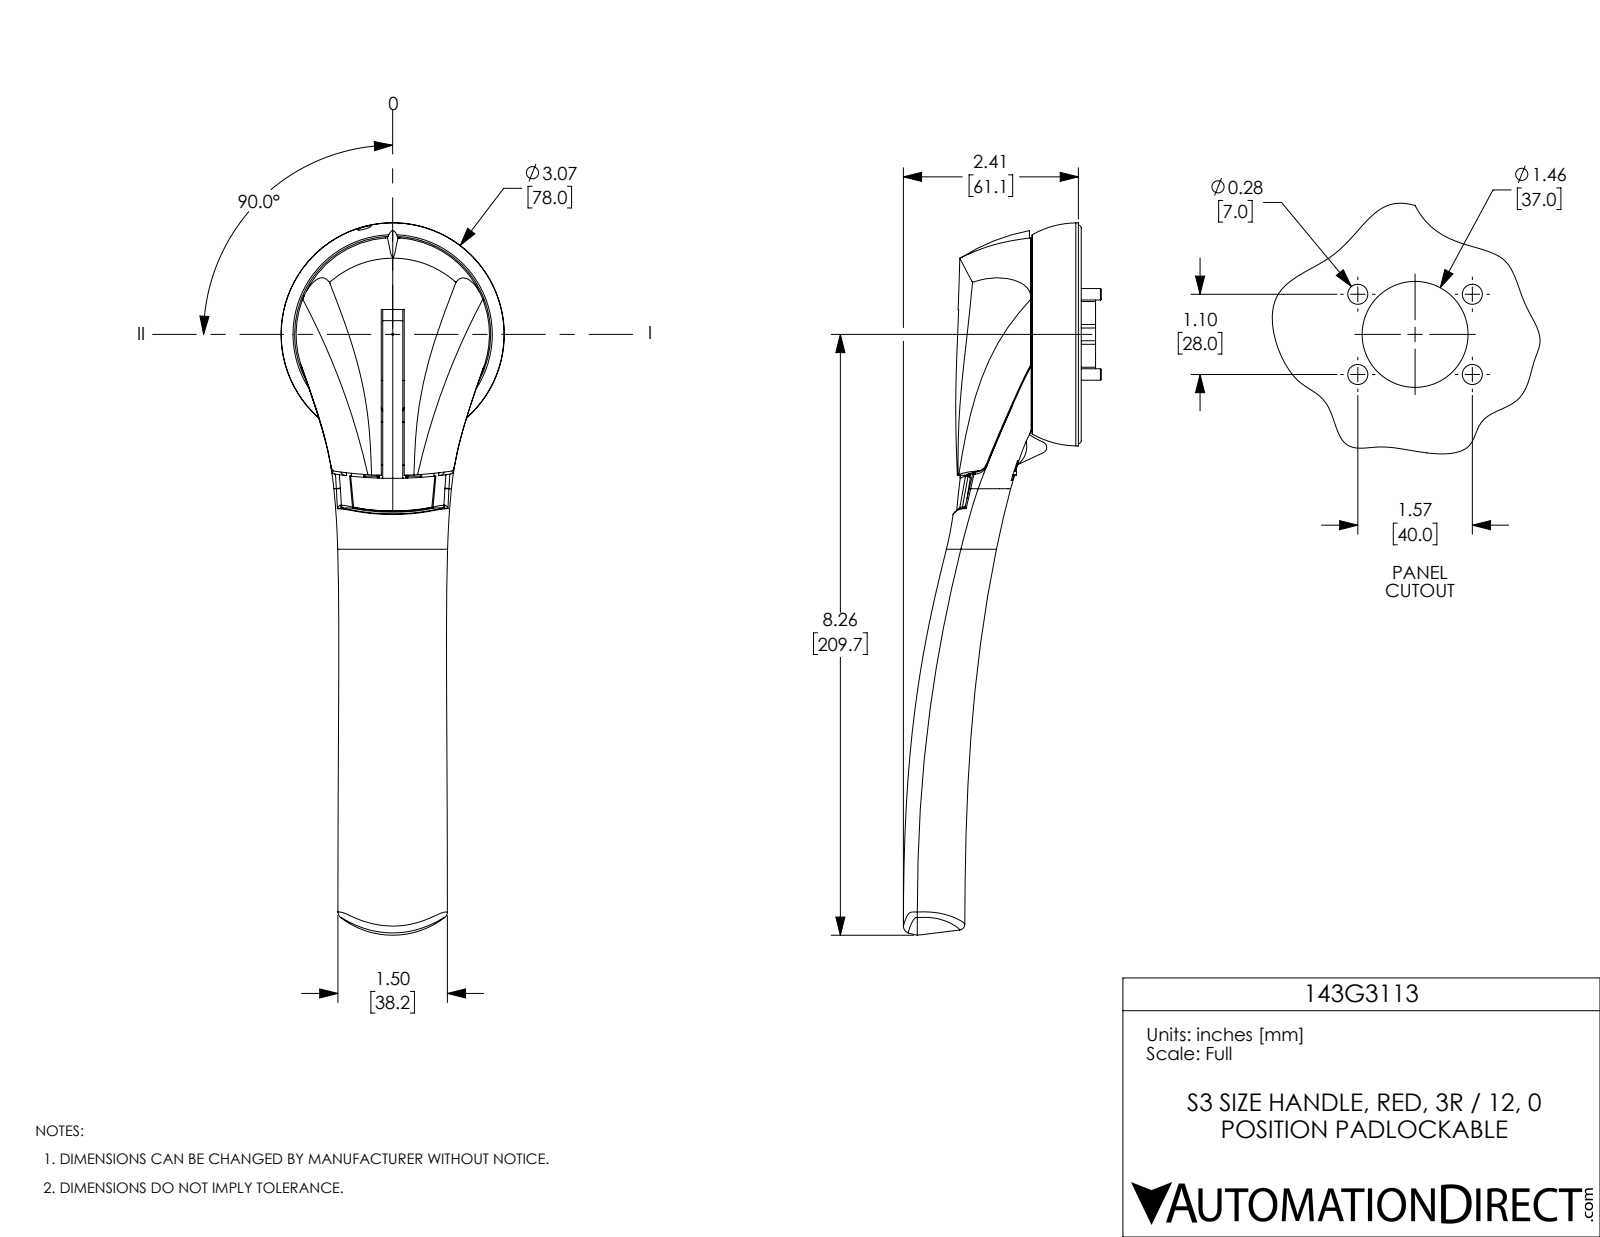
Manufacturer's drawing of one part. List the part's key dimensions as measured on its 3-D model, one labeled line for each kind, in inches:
Part name (STEP PRODUCT): 143G3113
STEP written by: SolidWorks 2017 (AUTOMOTIVE_DESIGN)
Units: inches
Bodies: 8 solids, 1514 faces (806 planar, 544 cylindrical, 164 other)
Overall size (bounding box): 9.793 × 3.07 × 2.721
Volume: 12.91 in³ · Surface area: 100.4 in²
Round holes (diameter × count): ⌀0.157 ×6, ⌀0.339 ×4, ⌀0.425 ×4, ⌀0.03 ×3, ⌀0.169 ×2, ⌀0.362 ×2, ⌀0.118 ×1, ⌀0.189 ×1, ⌀2.992 ×1
Round bosses / shafts (diameter × count): ⌀0.02 ×11, ⌀0.335 ×4, ⌀0.315 ×4, ⌀0.089 ×3, ⌀0.069 ×3, ⌀0.228 ×2, ⌀2.819 ×1, ⌀2.701 ×1
Partial cylindrical surfaces — rounded edges, fillets, slot ends (radius × count): R0.01 ×221, R0.015 ×20, R0.034 ×20, R0.03 ×15, R0.039 ×4, R0.025 ×3, R5.437 ×3, R0.079 ×2
Main face-to-face distances: 0.024, 0.701, 0.713, 0.689, 0.035, 0.276, 0.102, 0.173, 0.244, 0.047
Hole centre spacings: 0.961, 0.309, 0.669, 1.098, 1.102, 1.203, 1.575, 1.881
